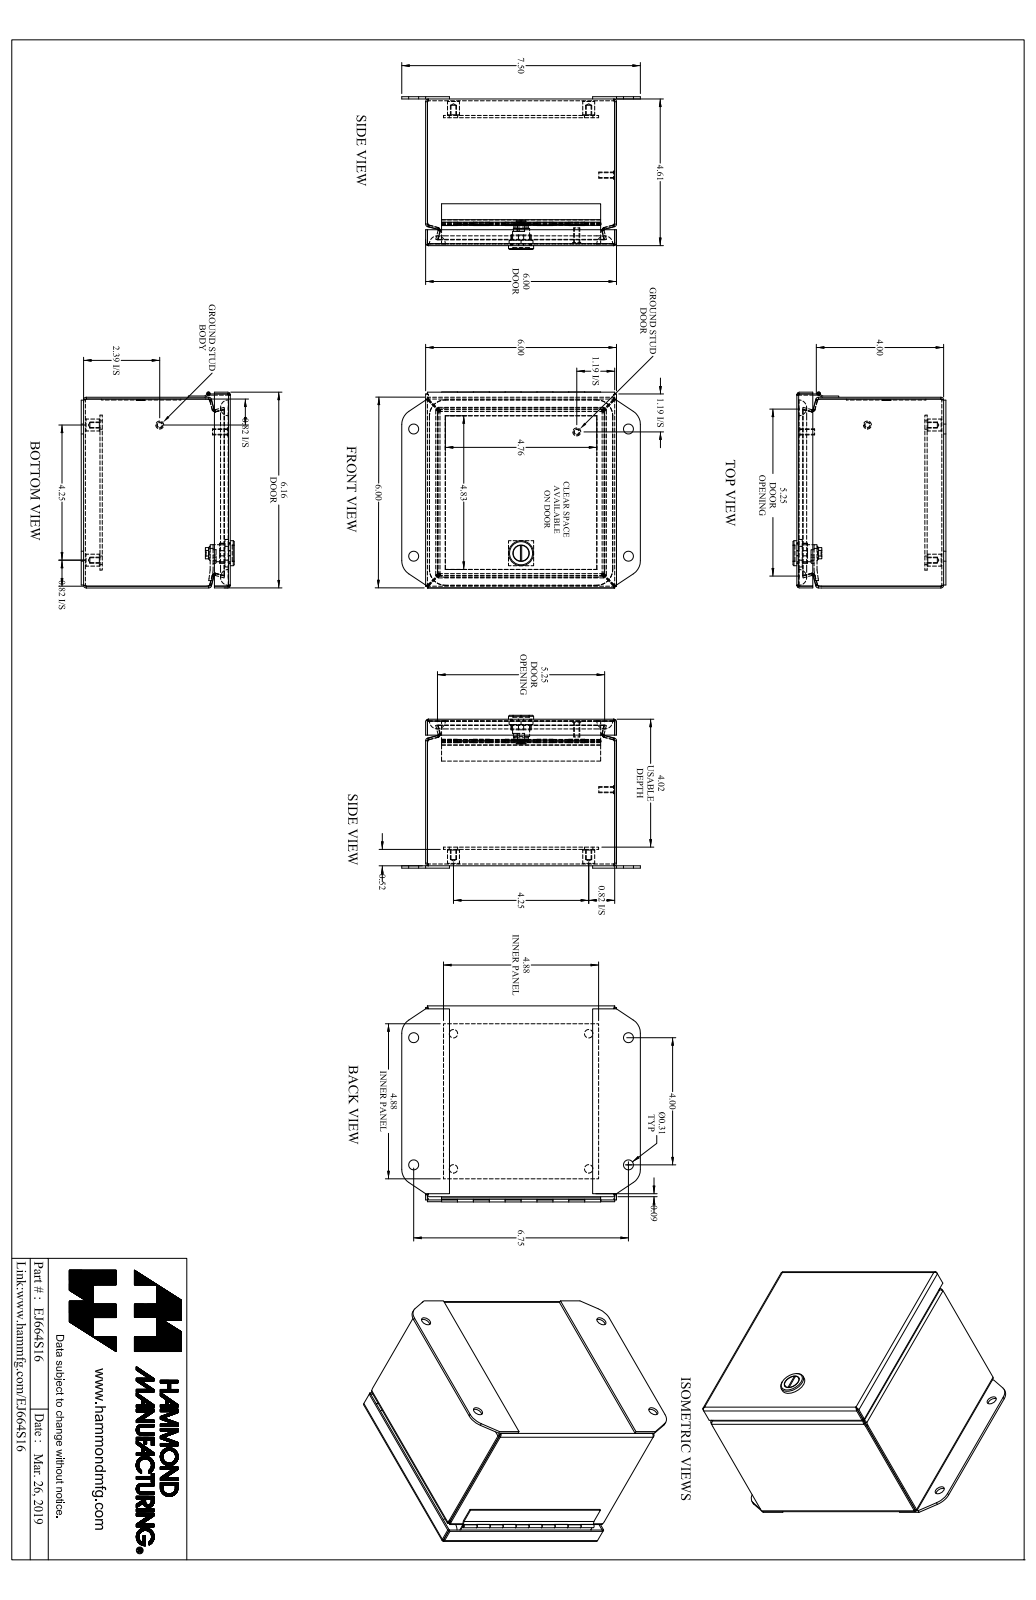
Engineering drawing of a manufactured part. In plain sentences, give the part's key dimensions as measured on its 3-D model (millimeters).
The part is named "EJ664S16_Default". Its 3-D file was written by "SolidWorks 2019 (CONFIG_CONTROL_DESIGN)". It is 16 solids with 532 faces: 278 planar, 174 cylindrical and 80 other. Overall it measures 190.5 by 156.6 by 122 millimeters. Its volume is 269 600 cubic millimeters and its surface area 348 600 square millimeters. Round holes: 4 of diameter 4, 4 of diameter 6.7, 4 of diameter 8, 1 of diameter 1.3, 1 of diameter 13.1. Round bosses or shafts: 4 of diameter 9.5, 2 of diameter 6.4, 2 of diameter 4.8, 1 of diameter 20, 1 of diameter 13.6, 1 of diameter 12.6, 1 of diameter 11, 1 of diameter 2.5. Partial cylindrical surfaces (rounded edges, fillets, slot ends): 16 of radius 0.7, 16 of radius 2.2, 12 of radius 7.1, 4 of radius 6.4, 4 of radius 12.7, 4 of radius 12.7, 2 of radius 1.5, 1 of radius 0.8. The main face-to-face distances are 1.4, 151, 115.7, 149.5, 152.4, 1.8, 15, 117.1, 114.2, 104. The hole center spacings are 31.9, 139.8, 54.3, 85.8, 101.6, 108, 108, 109.5.
